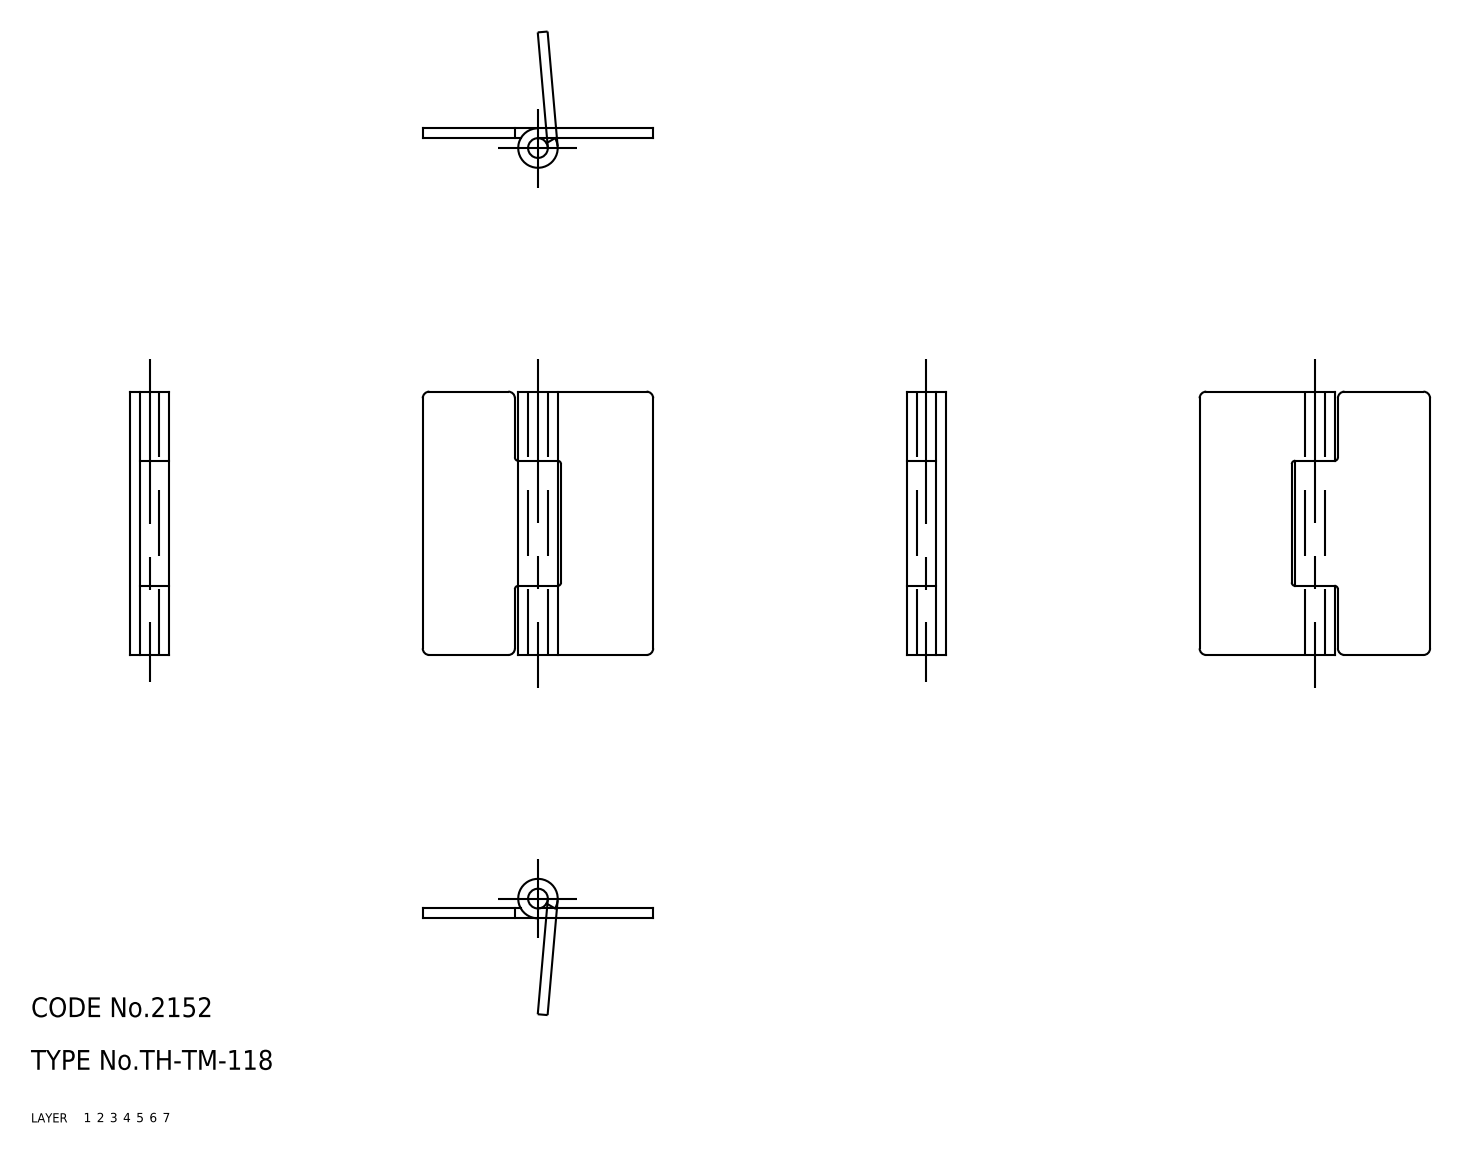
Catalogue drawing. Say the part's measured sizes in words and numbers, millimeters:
The part is named "hinge piece_B; hinge piece_A; shaft; TH_TM_118_21171_36". Its 3-D file was written by "CADfix (AUTOMOTIVE_DESIGN)". It is 3 solids with 36 faces: 0 planar, 0 cylindrical and 36 other. Overall it measures 40 by 35 by 6 millimeters. Its volume is 2 876 cubic millimeters and its surface area 4 305 square millimeters.
